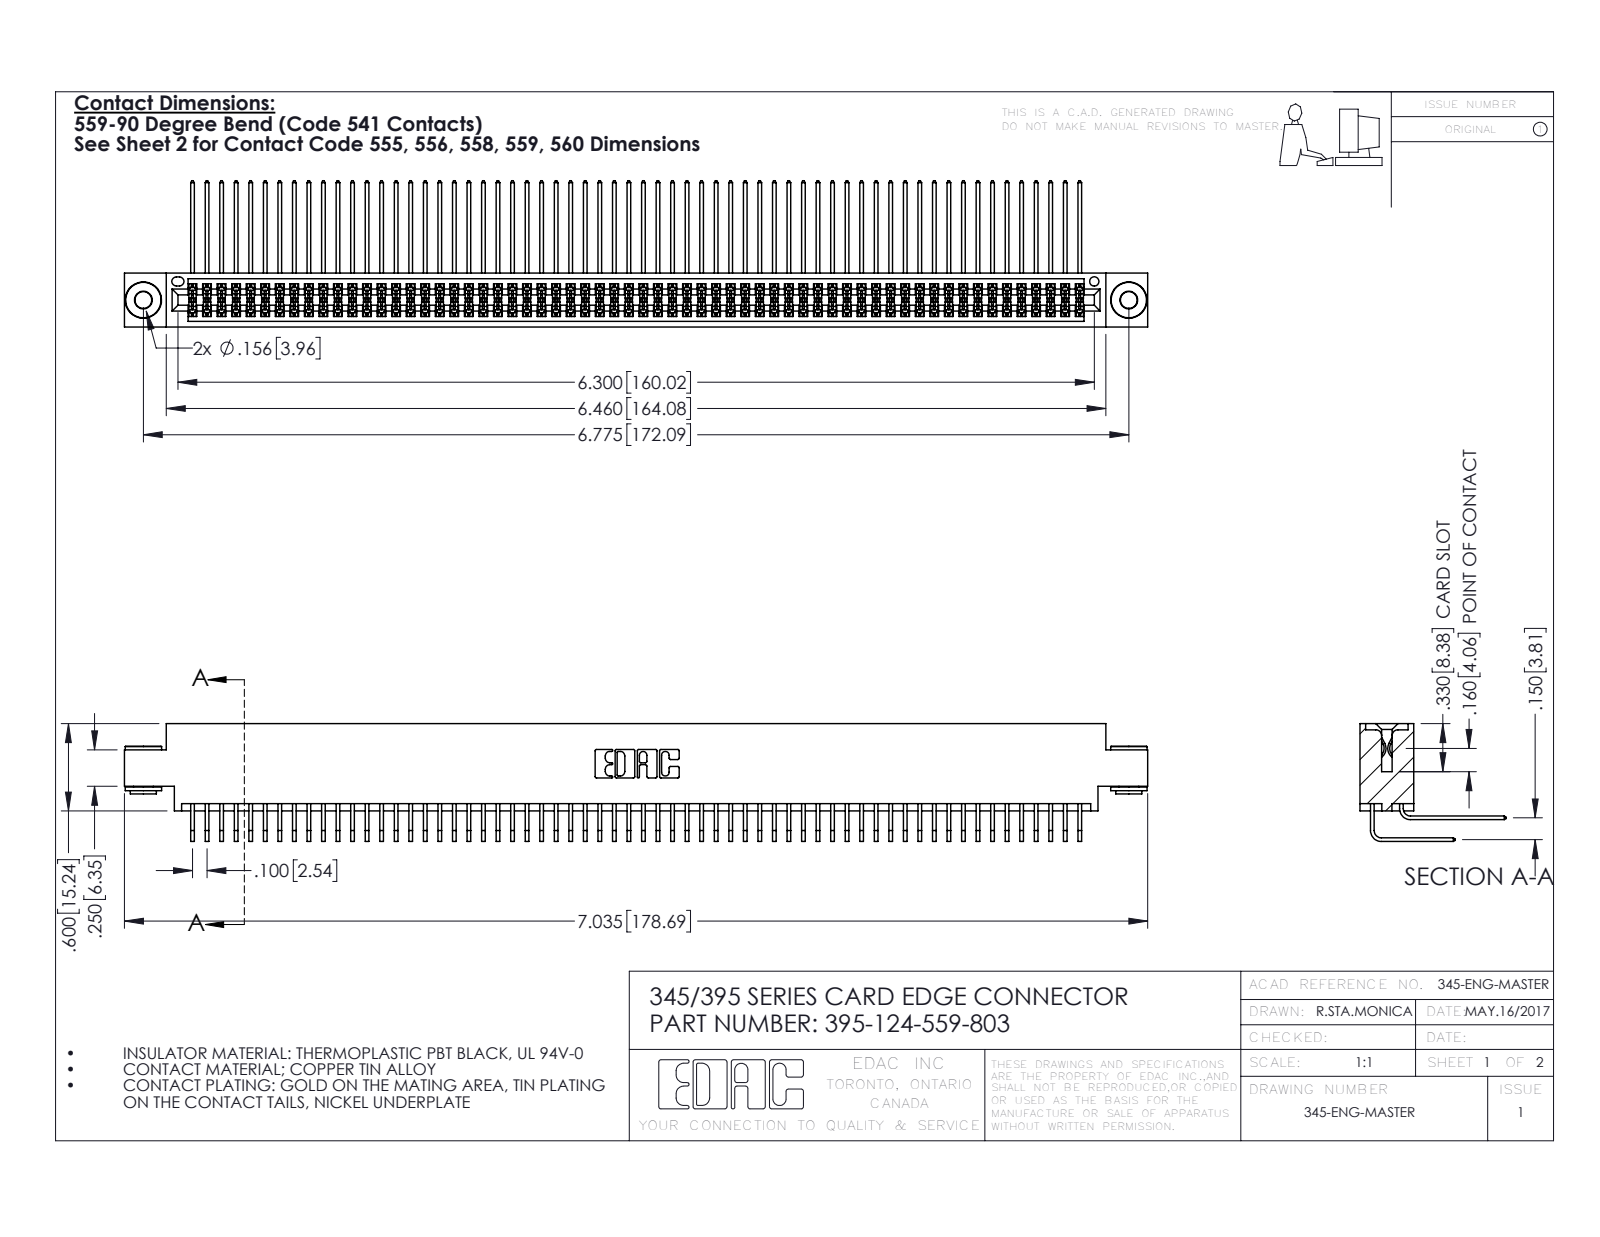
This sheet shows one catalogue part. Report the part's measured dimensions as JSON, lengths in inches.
{"part_name": "345-292-001_558 559 Tail - 1; 345-250-002_345-250-002-102; 395-124-559-803; 345-292-001_559 Tail - 2 (+1 more)", "step_written_by": "SolidWorks 2016 (CONFIG_CONTROL_DESIGN)", "units": "inches", "bodies": {"solids": 127, "faces": 6616, "planar": 4434, "cylindrical": 2174, "other": 8}, "overall_size": [7.035, 1.005, 0.809], "volume_in3": 1.108, "surface_area_in2": 47.97, "round_holes": [[0.116, 2], [0.156, 2], [0.064, 1]], "round_bosses_or_shafts": [[0.25, 2], [0.18, 2], [0.136, 2]], "partial_cylinders_radius": [[0.006, 186], [0.01, 22], [0.007, 6], [0.031, 6], [0.026, 3], [0.014, 2], [0.019, 2], [0.022, 2]], "face_to_face_distances": [0.072, 0.298, 0.37, 0.2, 0.098, 0.272, 0.025, 0.225, 0.175, 0.15], "hole_center_spacings": [0.27, 6.539, 6.775]}
